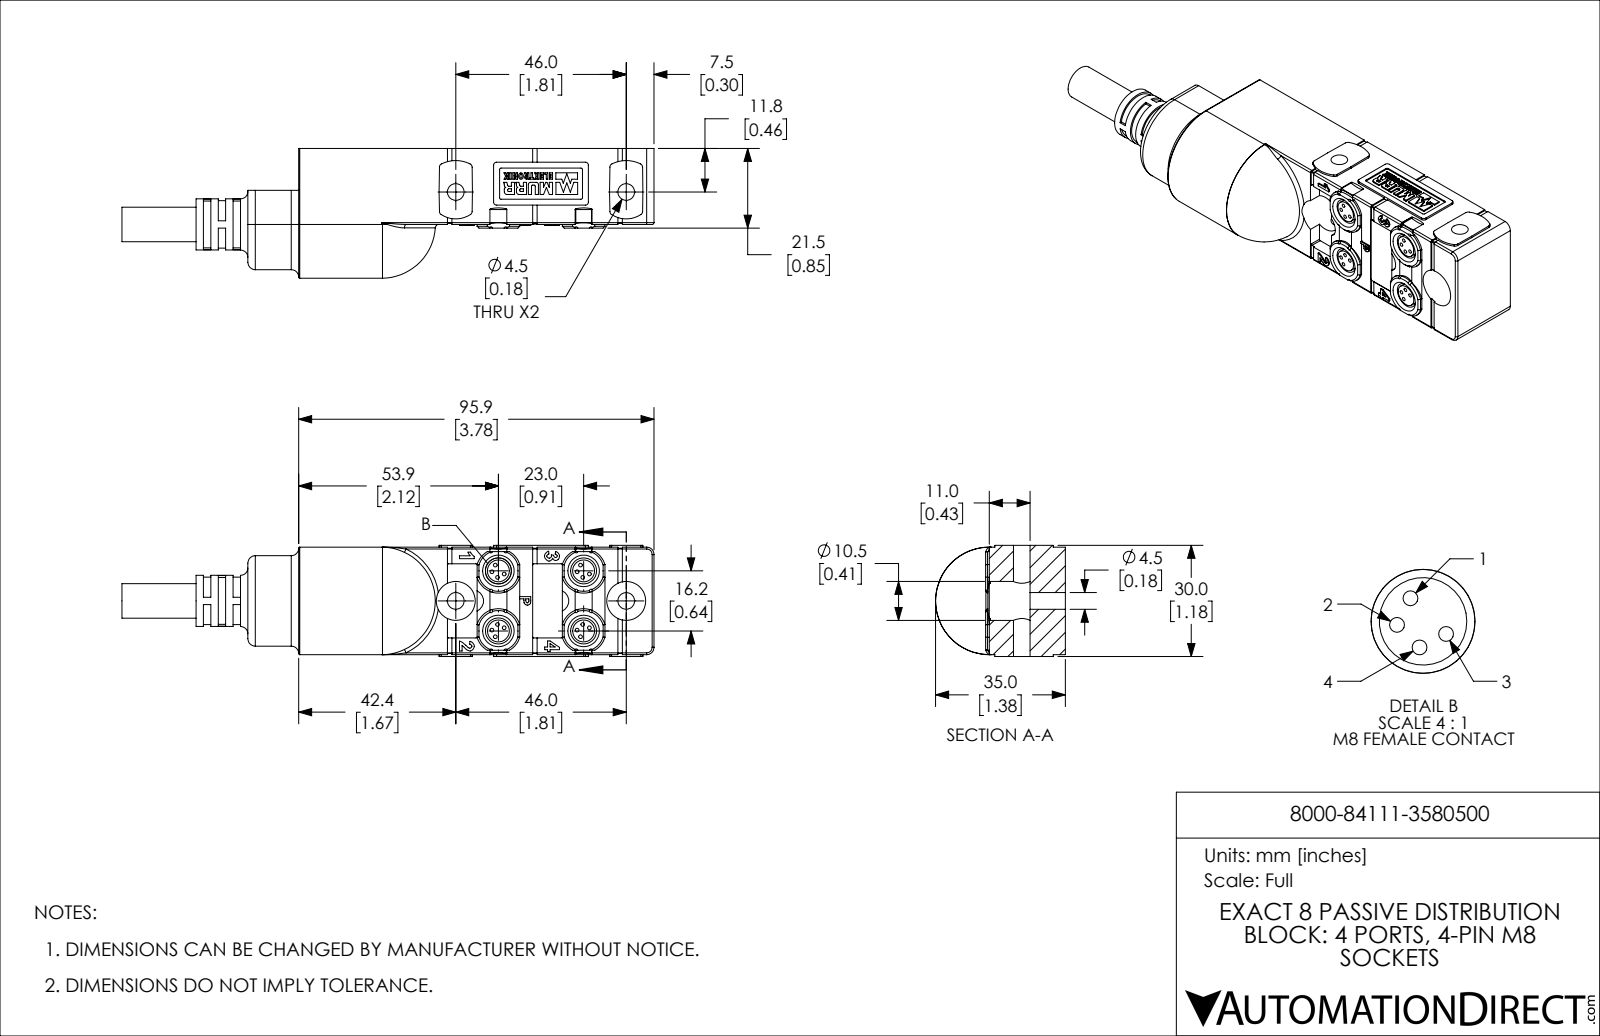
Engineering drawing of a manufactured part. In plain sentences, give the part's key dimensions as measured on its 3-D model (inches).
The part is named "8000-84111-3580500". Its 3-D file was written by "SolidWorks 2019 (CONFIG_CONTROL_DESIGN)". It is 1 solid with 983 faces: 585 planar, 293 cylindrical and 105 other. Overall it measures 5.654 by 1.378 by 1.181 inches. Its volume is 4.519 cubic inches and its surface area 25.71 square inches. Round holes: 16 of diameter 0.039, 4 of diameter 0.177, 4 of diameter 0.276, 2 of diameter 0.413. Round bosses or shafts: 4 of diameter 0.232, 1 of diameter 0.543, 1 of diameter 0.504, 1 of diameter 0.449, 1 of diameter 0.366. Partial cylindrical surfaces (rounded edges, fillets, slot ends): 19 of radius 0.02, 12 of radius 0.008, 10 of radius 0.012, 8 of radius 0.039, 6 of radius 0.079, 6 of radius 0.394, 4 of radius 0.012, 4 of radius 0.012. The main face-to-face distances are 1.142, 0.02, 1.161, 0.807, 0.795, 0.433, 0.362, 0.445, 1.181, 3.776. The hole center spacings are 0.07, 0.906, 0.08, 0.133, 0.085, 0.134, 0.54, 0.554.
